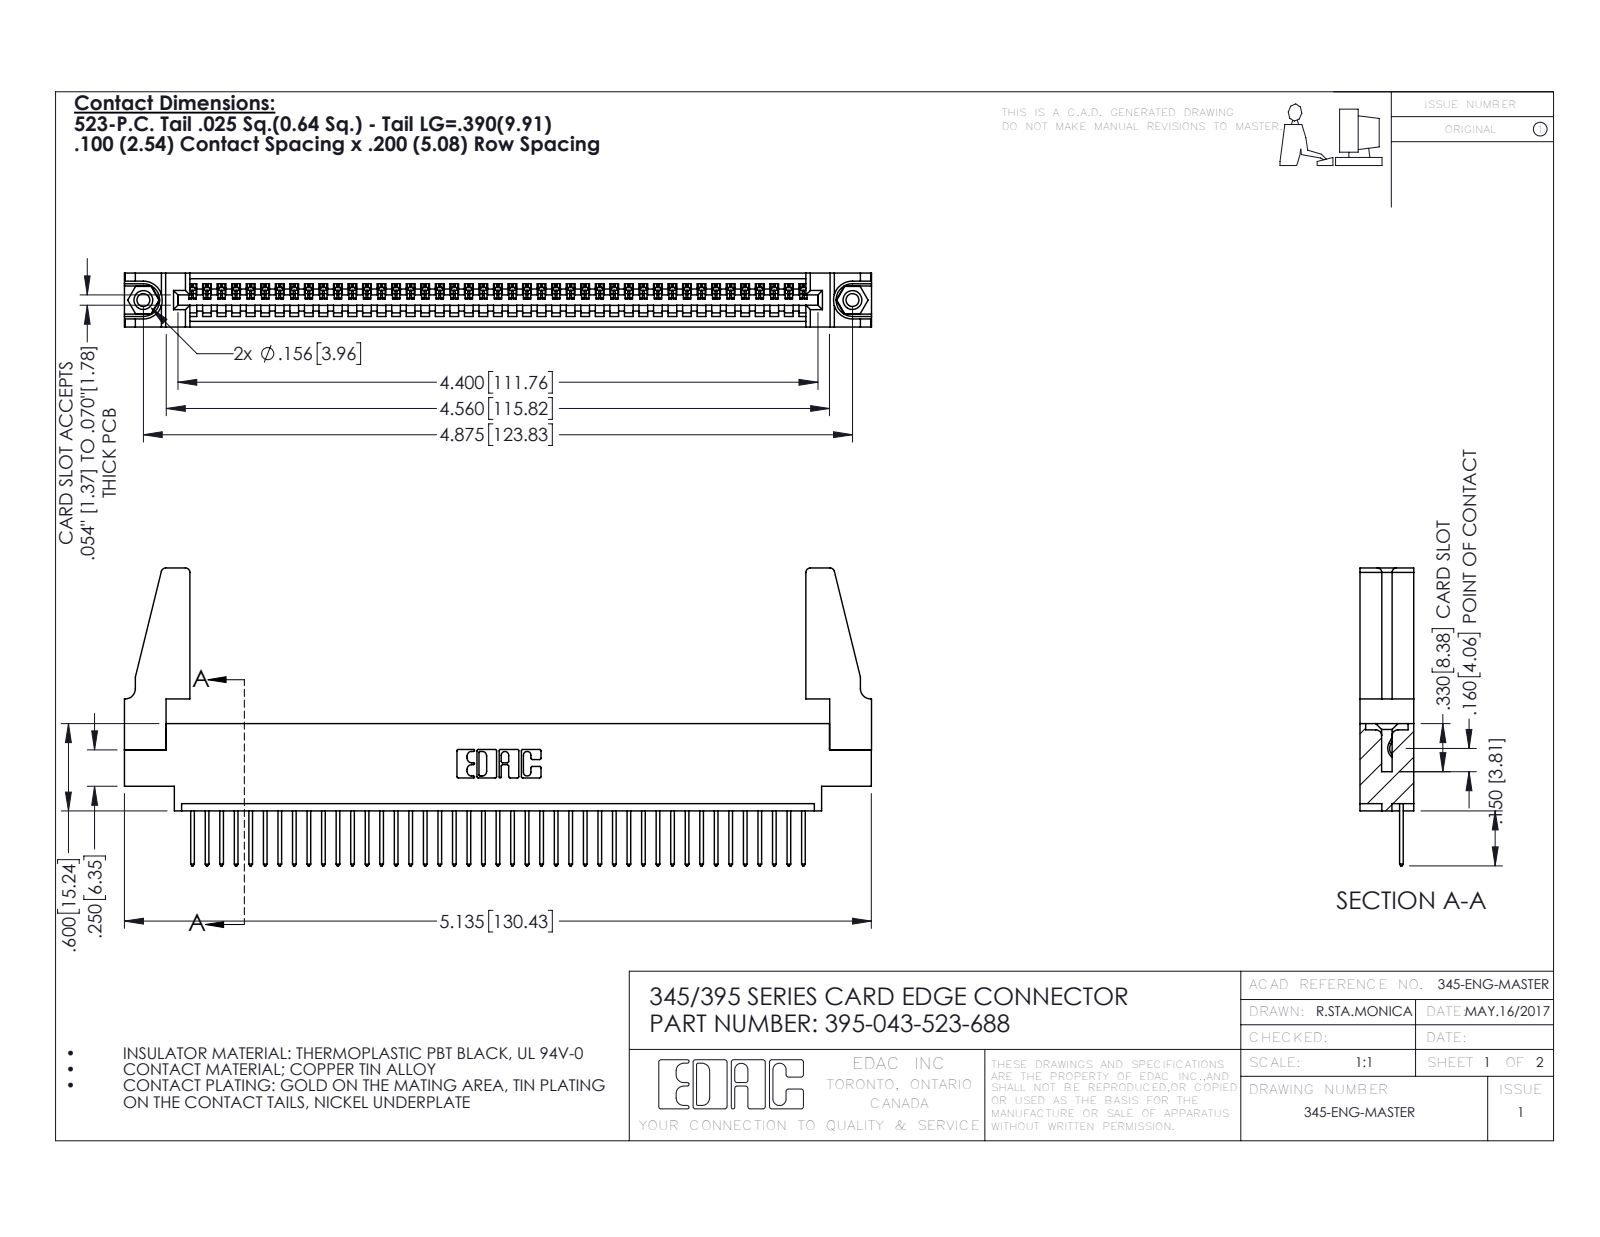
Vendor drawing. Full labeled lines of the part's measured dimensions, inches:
Part name (STEP PRODUCT): 395-043-523-688; 345 Part_0.170 Offset - 0.156 Dia-TH; 345-292-001_345-293-123; 345-250-001_345-250-001-102 (+1 more)
STEP written by: SolidWorks 2016 (CONFIG_CONTROL_DESIGN)
Units: inches
Bodies: 48 solids, 2748 faces (1876 planar, 856 cylindrical, 16 other)
Overall size (bounding box): 5.136 × 2.047 × 0.37
Volume: 0.947 in³ · Surface area: 30.41 in²
Round holes (diameter × count): ⌀0.089 ×2, ⌀0.125 ×2, ⌀0.156 ×2, ⌀0.064 ×1
Round bosses / shafts (diameter × count): ⌀0.155 ×2
Partial cylindrical surfaces — rounded edges, fillets, slot ends (radius × count): R0.006 ×86, R0.01 ×86, R0.01 ×22, R0.03 ×8, R0.007 ×6, R0.031 ×6, R0.026 ×3, R0.031 ×2
Main face-to-face distances: 0.072, 0.298, 0.37, 0.098, 0.272, 0.025, 0.2, 0.225, 0.175, 0.149
Hole centre spacings: 0.27, 4.639, 4.875
